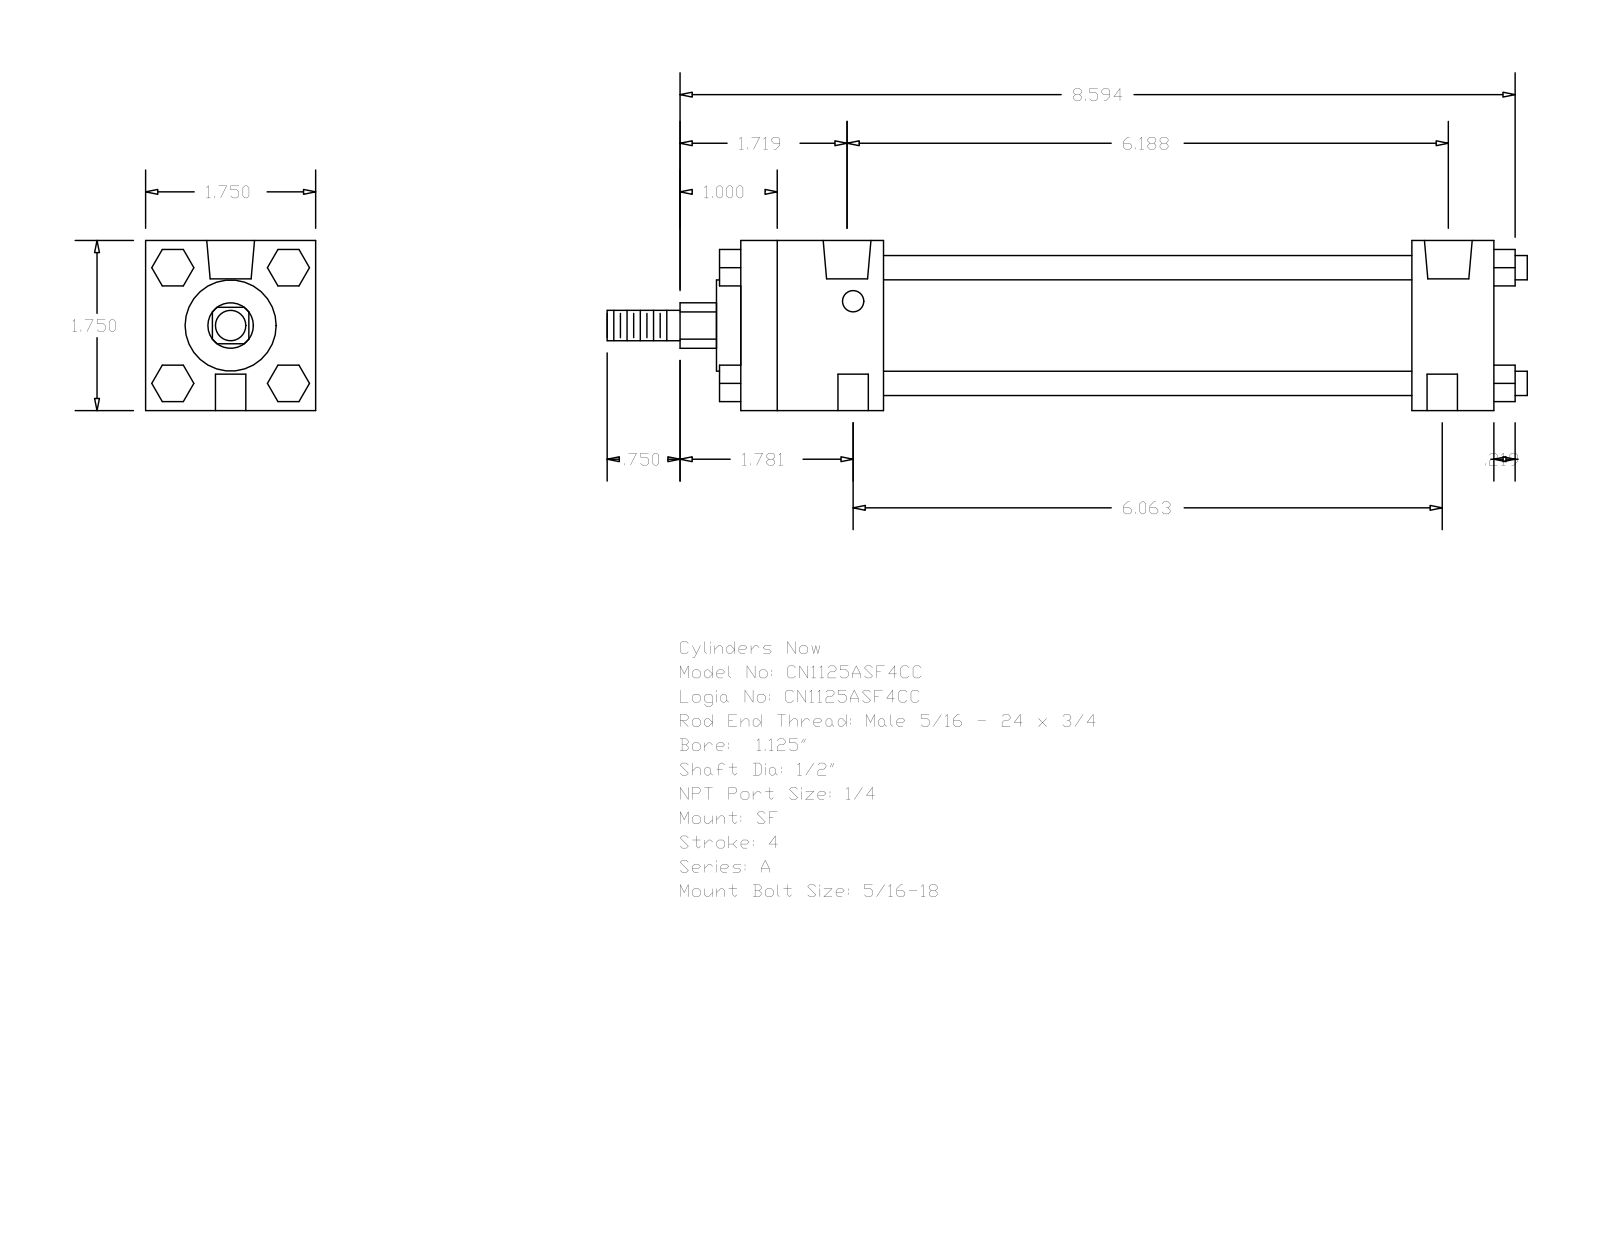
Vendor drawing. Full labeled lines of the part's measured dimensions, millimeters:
Part name (STEP PRODUCT): A_SF__0112_0.5
STEP written by: GSSL Pune (CONFIG_CONTROL_DESIGN)
Units: millimetres
Bodies: 0 solids, 120 faces (92 planar, 28 cylindrical, 0 other)
Overall size (bounding box): 240.51 × 44.45 × 44.45
Round holes (diameter × count): ⌀5.56 ×2, ⌀7.94 ×2, ⌀12.49 ×2
Round bosses / shafts (diameter × count): ⌀6.35 ×4, ⌀31.88 ×1, ⌀23.81 ×1, ⌀12.7 ×1, ⌀7.94 ×1
Partial cylindrical surfaces — rounded edges, fillets, slot ends (radius × count): R5.94 ×1
Main face-to-face distances: 44.46, 196.84, 175.41, 21.43, 37.3, 138.11, 159.54, 9.53, 5.59, 5.56
Hole centre spacings: 153.99, 1.58, 1.59, 155.57, 155.58, 157.16
